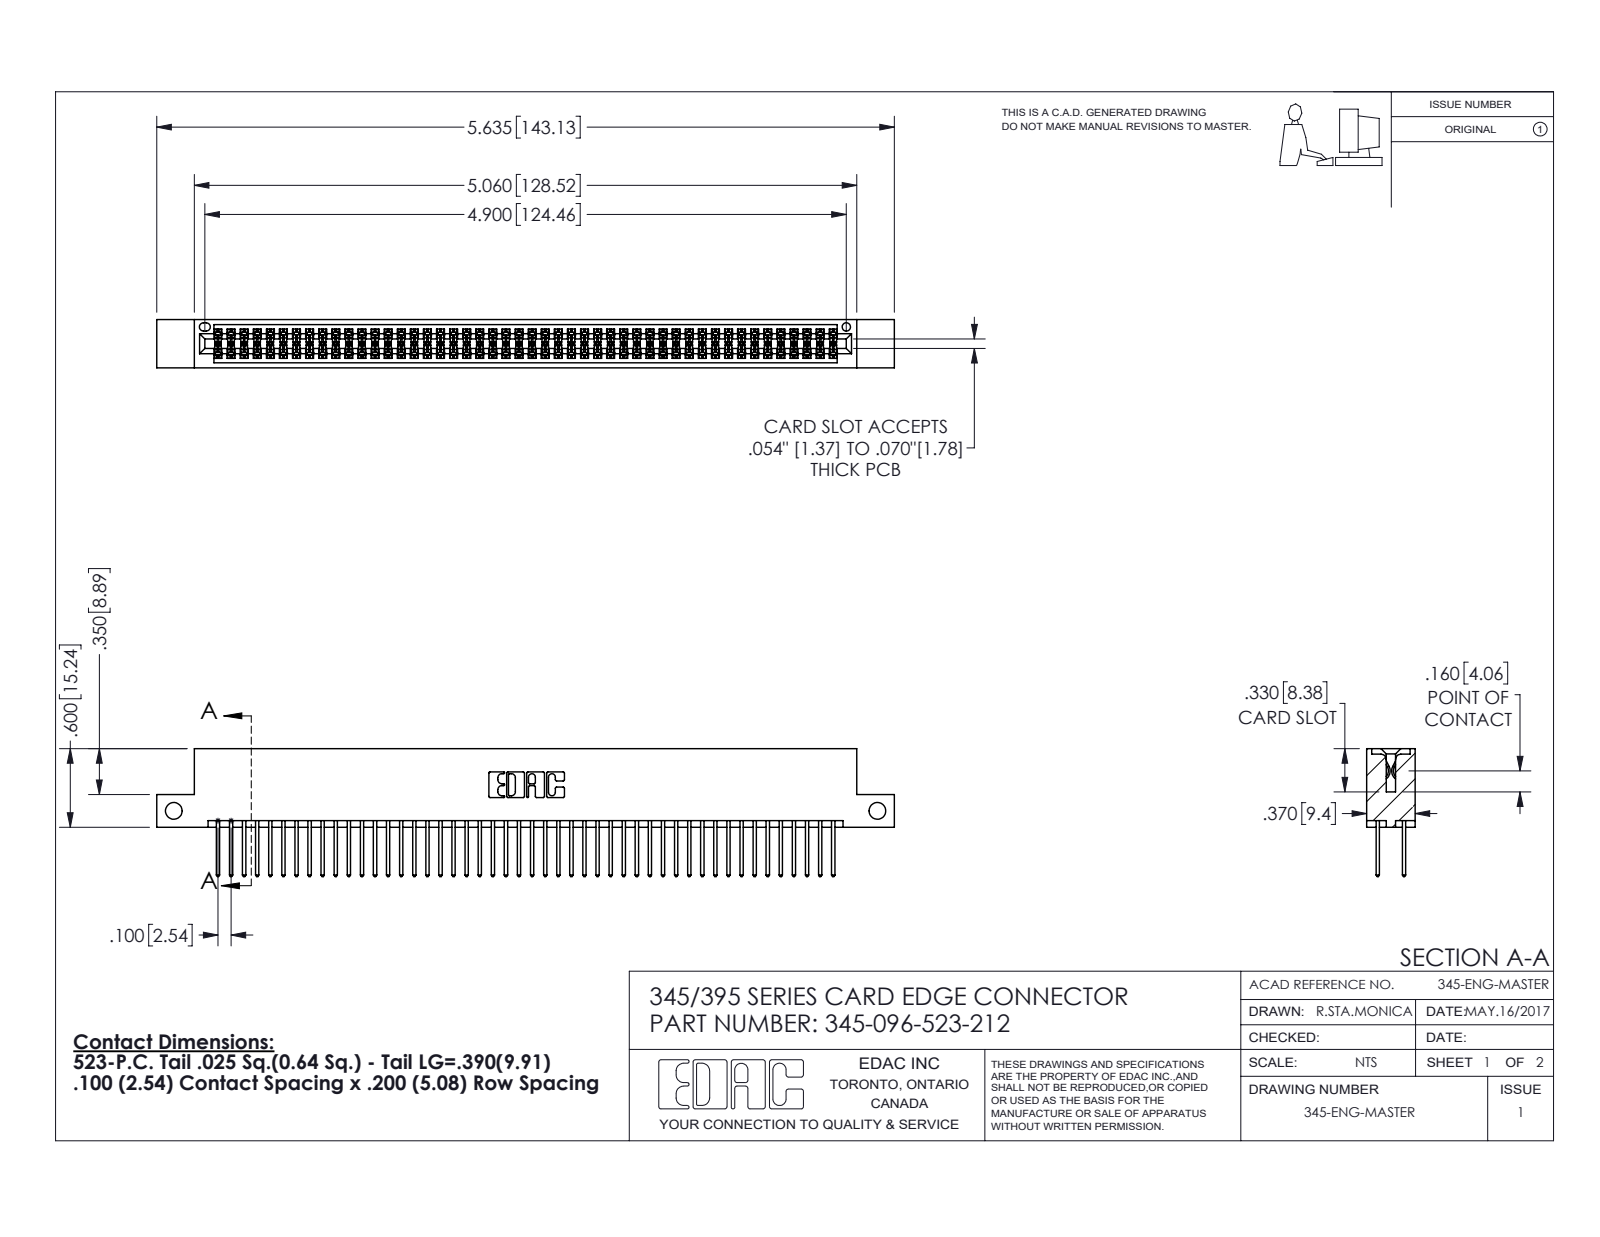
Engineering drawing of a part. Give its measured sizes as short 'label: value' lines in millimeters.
name: 345 Part_Flush Mounting Lugs - Side Mount; 345-096-523-212; 345-292-001_345-293-123
written by: SolidWorks 2016 (CONFIG_CONTROL_DESIGN)
unit: mm
bodies: 97 solids, 4926 faces (3248 planar, 1678 cylindrical, 0 other)
size: 143.1 × 24.8 × 9.4
volume: 14 100 mm³; area: 21 660 mm²
holes: 2× ⌀3.3, 1× ⌀1.6
rounds: 144× R0.2, 96× R0.3, 22× R0.3, 6× R0.2, 6× R0.8, 3× R0.7, 2× R0.4, 2× R0.5
face distances: 7.6, 1.8, 5.1, 2.5, 6.9, 0.6, 9.4, 5.7, 4.4, 3.8
hole spacings: 136.5
